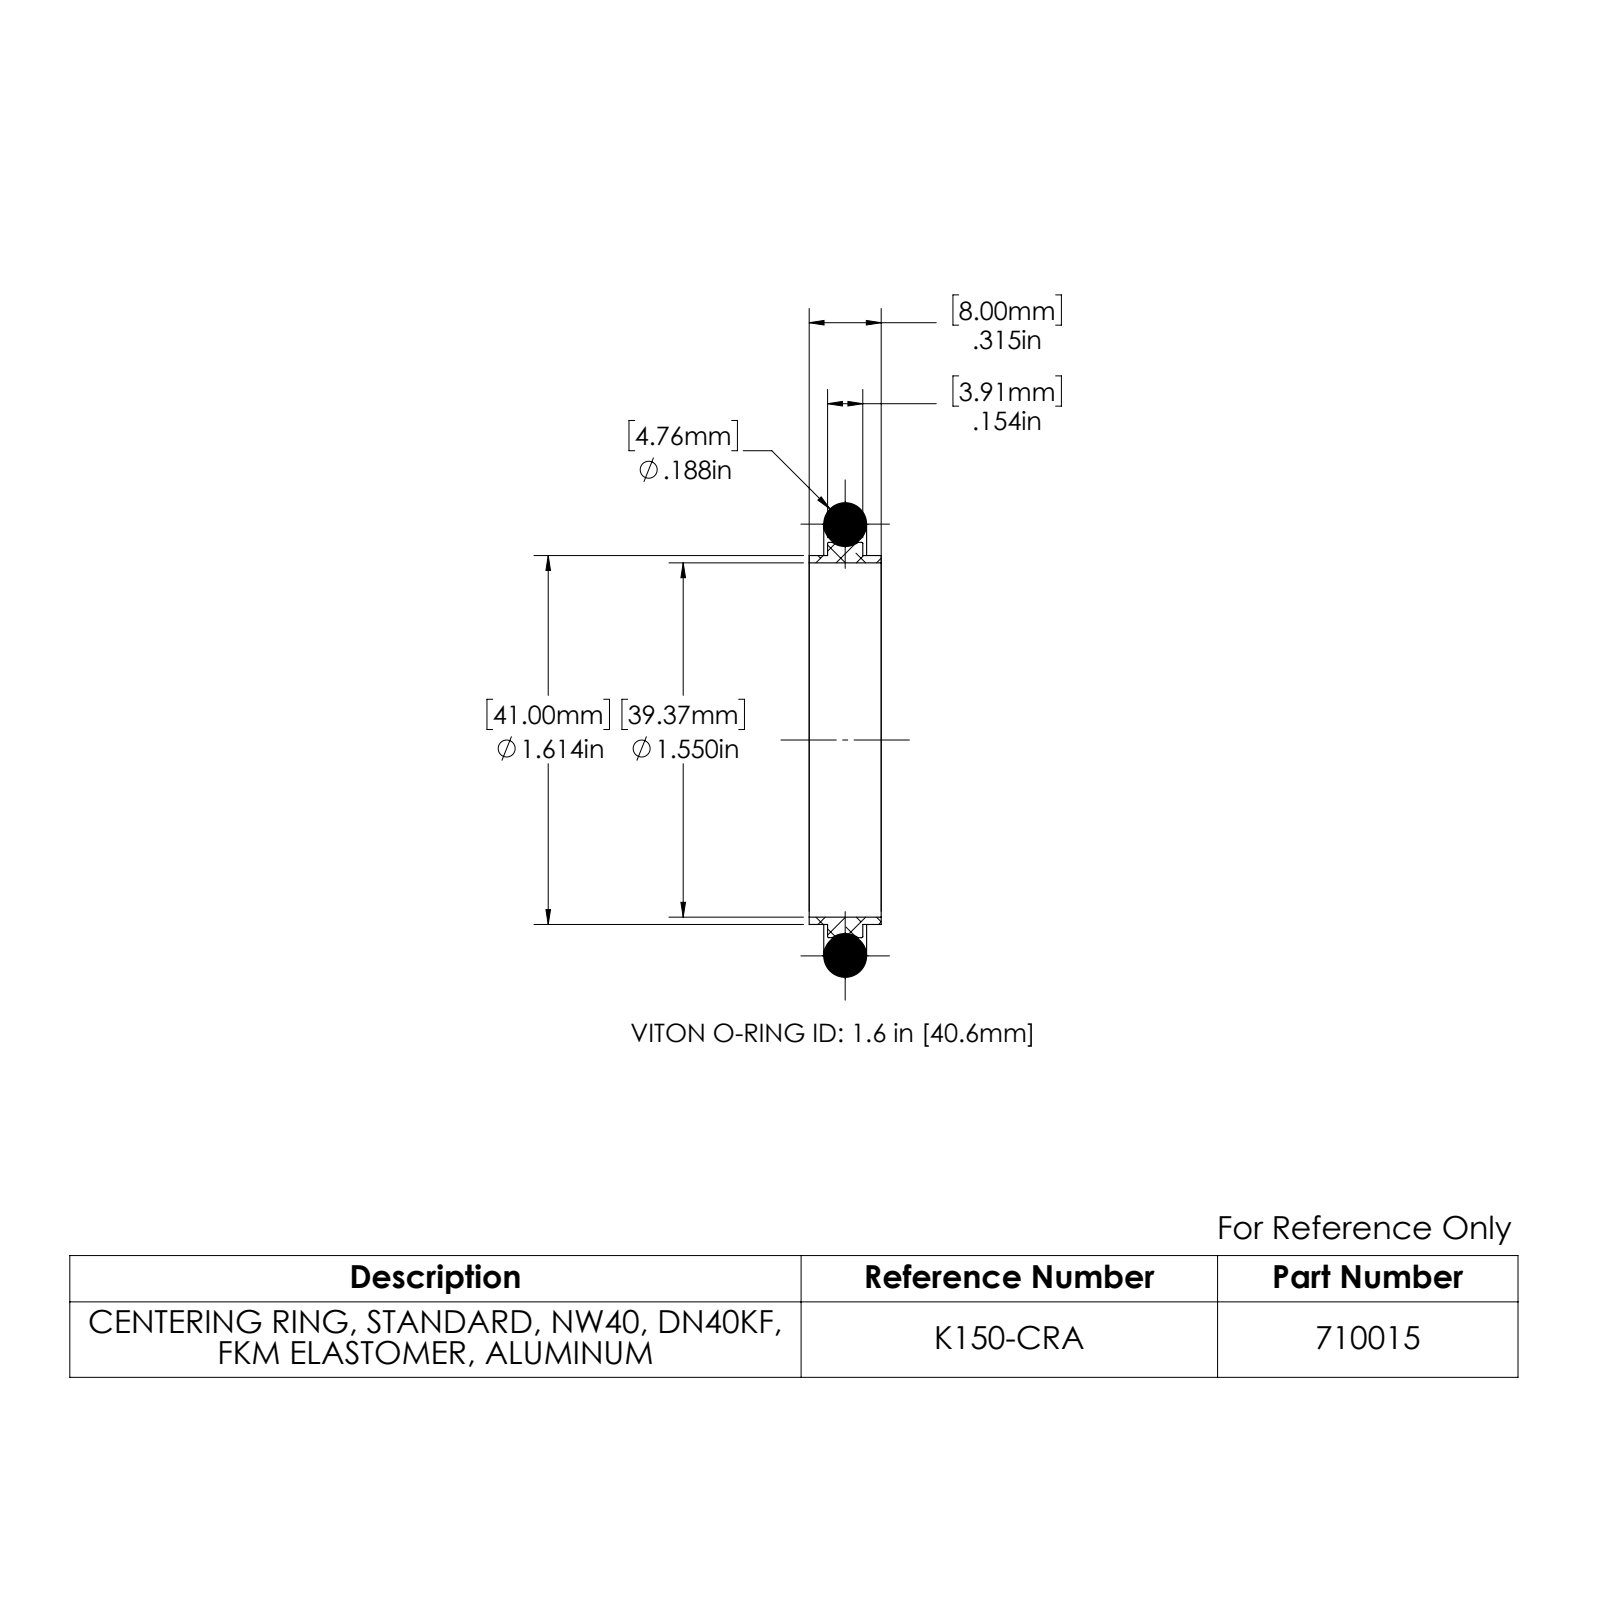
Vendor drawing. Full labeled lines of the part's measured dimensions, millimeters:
Part name (STEP PRODUCT): 710015
STEP written by: SolidWorks 2022 (AUTOMOTIVE_DESIGN)
Units: millimetres
Bodies: 2 solids, 30 faces (4 planar, 10 cylindrical, 16 other)
Overall size (bounding box): 52.7 × 52.7 × 8
Volume: 4 150 mm³ · Surface area: 4 914 mm²
Round holes (diameter × count): ⌀39.4 ×1
Round bosses / shafts (diameter × count): ⌀43.9 ×1, ⌀41 ×1
Main face-to-face distances: 2, 6, 3.9, 8
